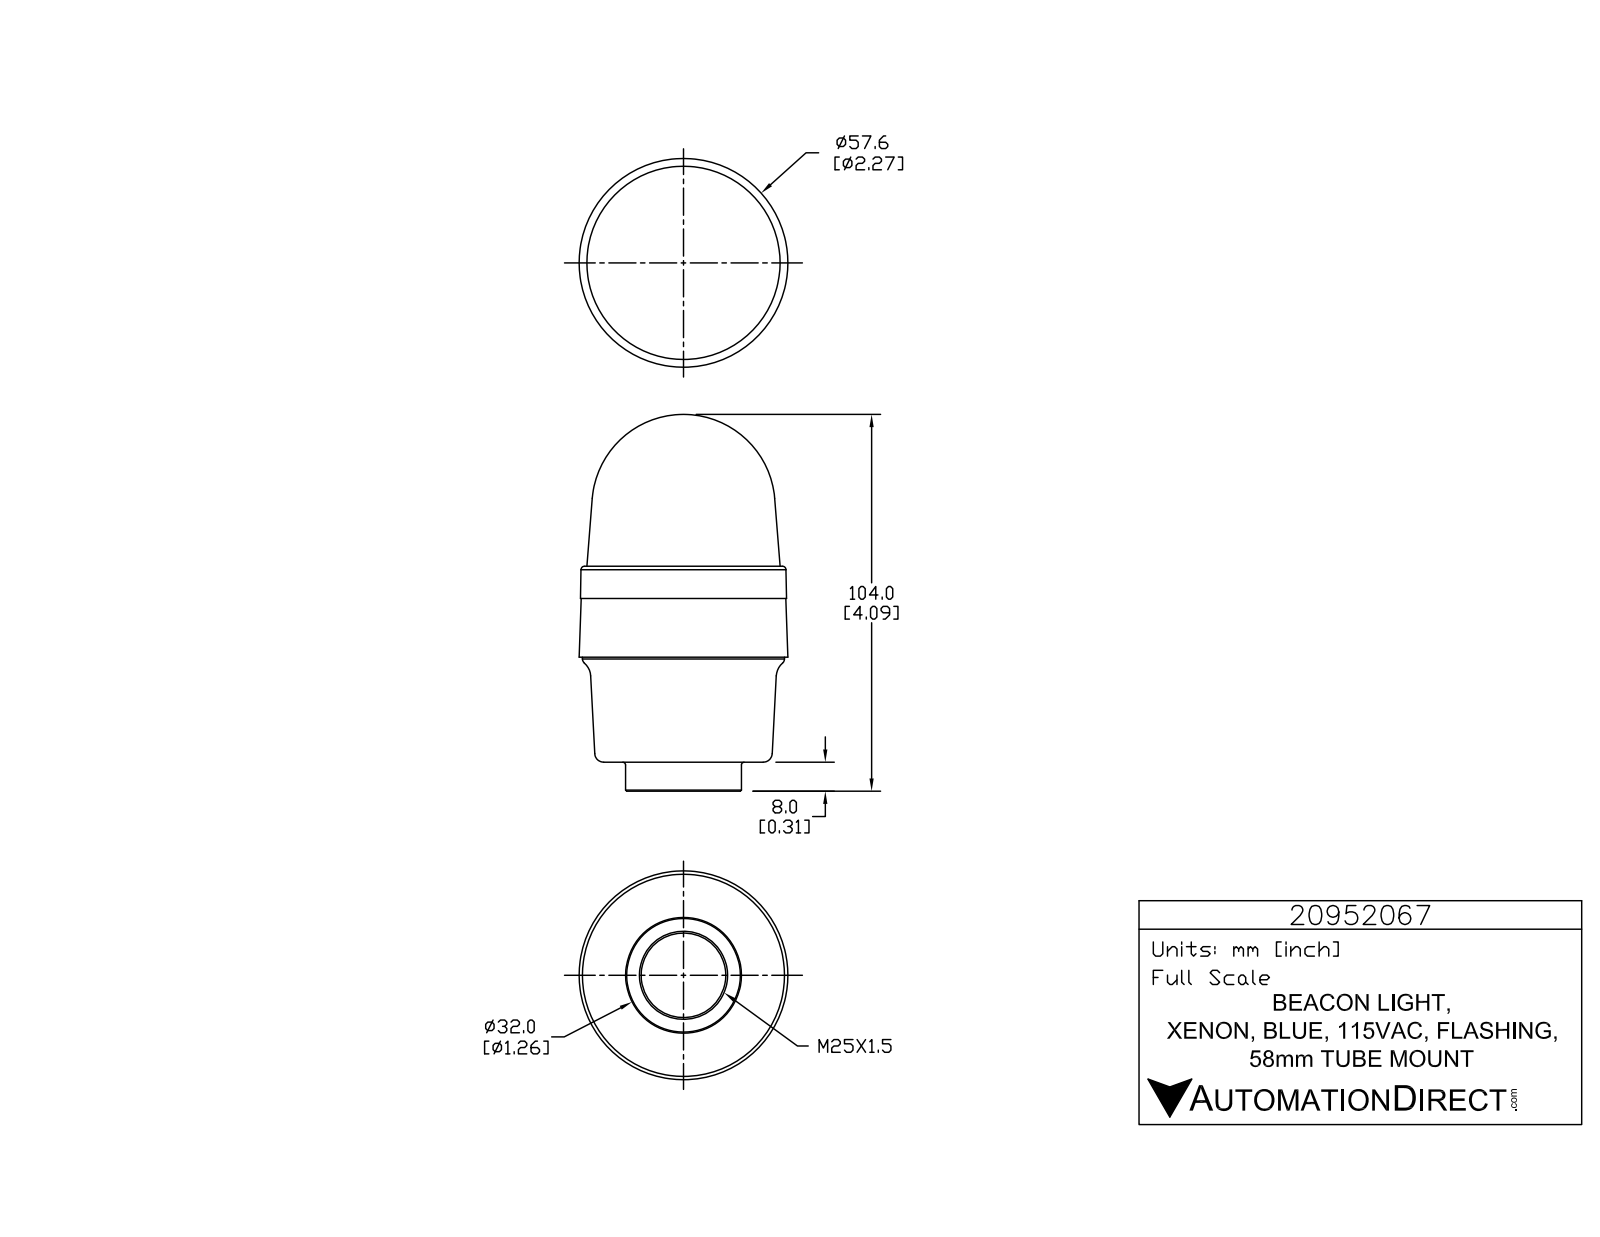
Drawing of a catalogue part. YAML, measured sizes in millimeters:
part_name: "20952067"
step_written_by: "SolidWorks 2015 (AUTOMOTIVE_DESIGN)"
units: millimeters
bodies: {solids: 1, faces: 791, planar: 525, cylindrical: 168, other: 98}
overall_size: [102.9, 57.6, 57.6]
volume: 192100
surface_area: 19310
round_holes:
  - {diameter: 1, count: 3}
  - {diameter: 23.4, count: 1}
round_bosses_or_shafts:
  - {diameter: 5.7, count: 3}
  - {diameter: 1.4, count: 3}
  - {diameter: 55.8, count: 1}
  - {diameter: 32, count: 1}
partial_cylinders:
  - {radius: 0.2, count: 6}
  - {radius: 0.2, count: 6}
  - {radius: 0.2, count: 6}
  - {radius: 3.3, count: 6}
  - {radius: 0.1, count: 3}
  - {radius: 0.1, count: 3}
  - {radius: 0.2, count: 3}
  - {radius: 0.2, count: 3}
face_to_face_distances: [8, 29, 37, 25.1, 54.1, 62.1, 8.9, 16.2, 45.2, 53.2]
